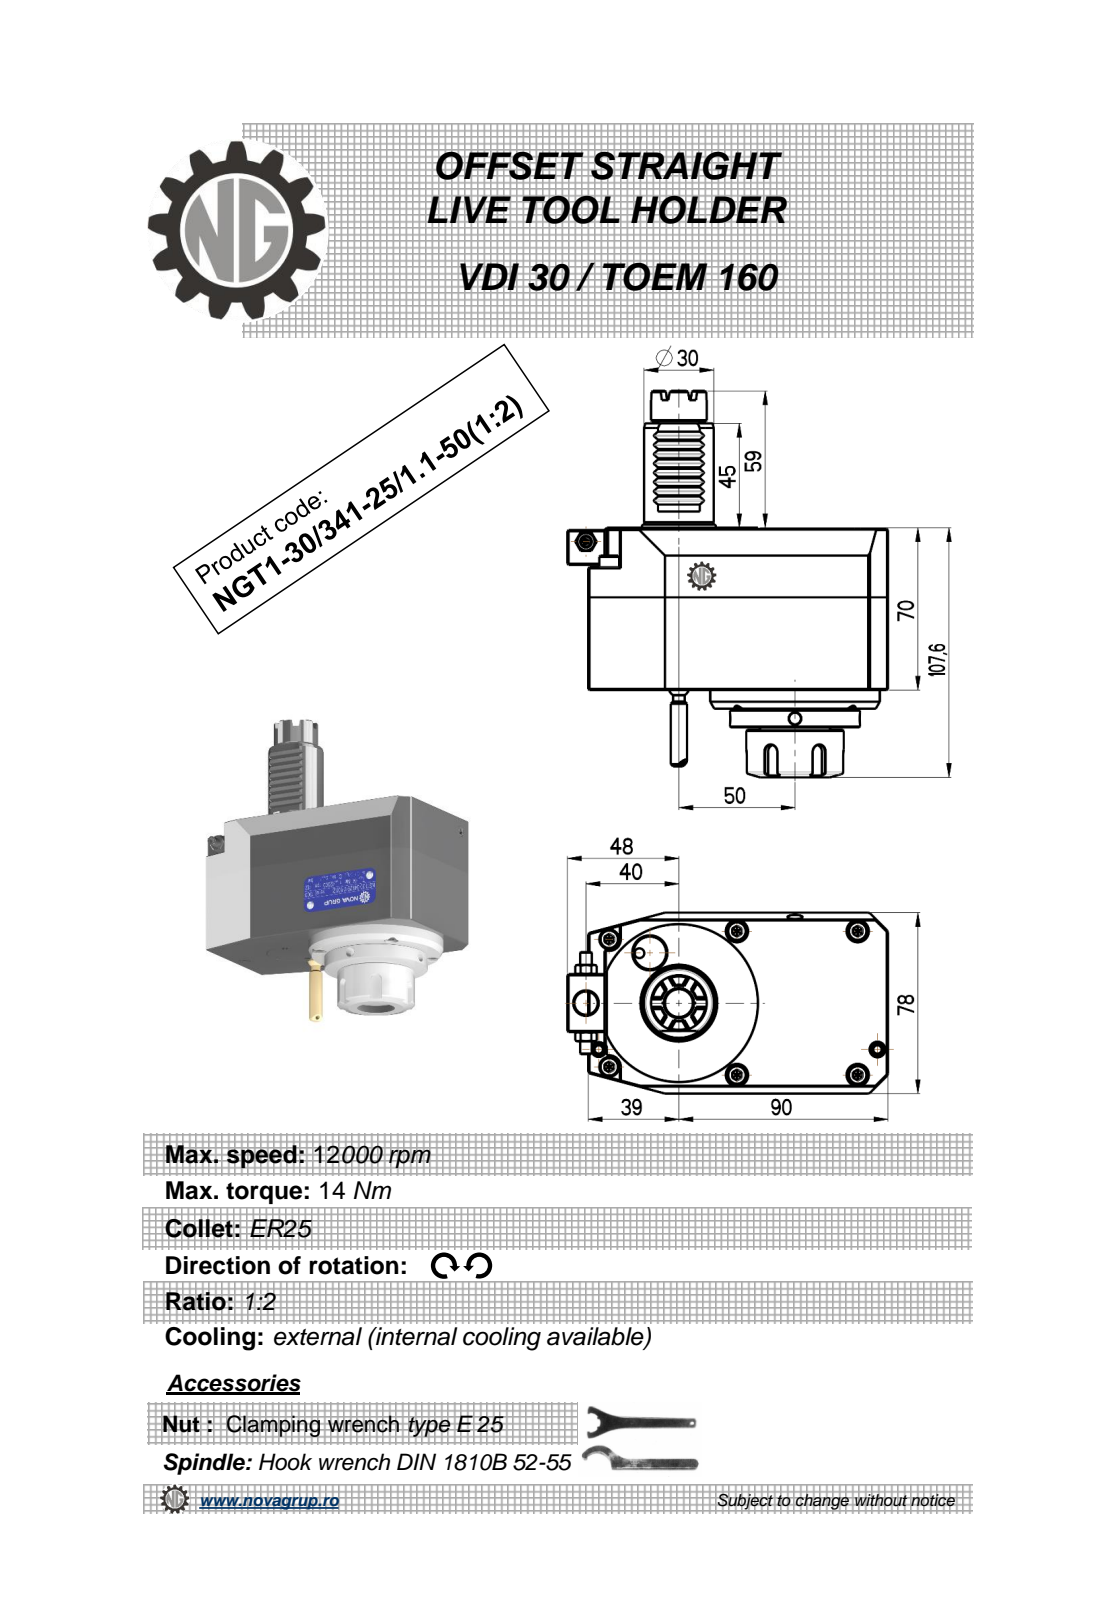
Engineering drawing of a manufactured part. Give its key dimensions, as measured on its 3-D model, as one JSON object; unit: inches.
{"part_name": "NGT1_30_341_25_1_1_50_1_2", "step_written_by": "PRO/ENGINEER BY PARAMETRIC TECHNOLOGY CORPORATION, 2010280 (CONFIG_CONTROL_DESIGN)", "units": "inches", "bodies": {"solids": 1, "faces": 439, "planar": 192, "cylindrical": 103, "other": 144}, "overall_size": [6.559, 5.433, 3.071], "volume_in3": 47.87, "surface_area_in2": 101.3, "round_holes": [[0.197, 2], [0.098, 1], [0.118, 1], [0.165, 1], [0.374, 1], [0.394, 1], [0.551, 1], [0.591, 1]], "round_bosses_or_shafts": [[0.315, 2], [0.197, 2], [2.874, 1], [2.205, 1], [1.654, 1], [1.299, 1], [1.181, 1], [0.945, 1]], "partial_cylinders_radius": [[0.006, 12], [0.01, 12], [0.012, 8], [0.118, 5], [0.177, 2], [0.299, 1]], "face_to_face_distances": [3.071, 2.756, 0.315, 5.079, 0.63, 3.386, 0.02, 2.717, 0.295, 3.091], "hole_center_spacings": [0.492, 0.846, 0.984, 1.378, 1.575, 1.788, 2.904, 4.644]}
